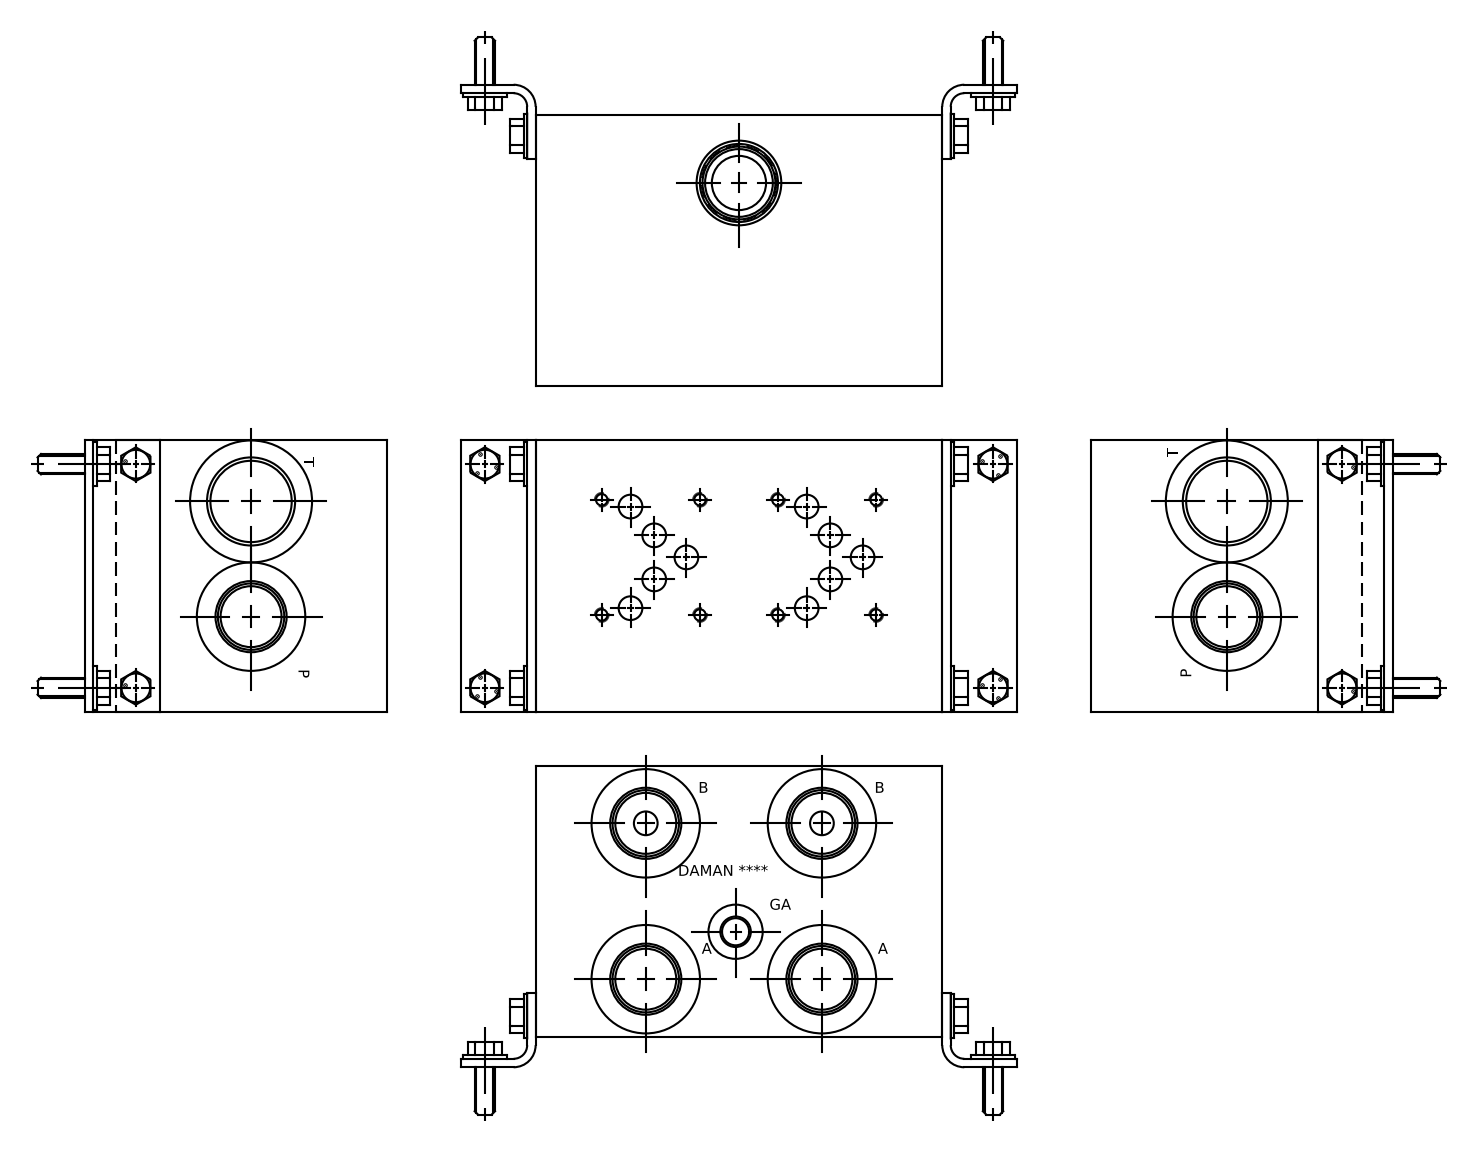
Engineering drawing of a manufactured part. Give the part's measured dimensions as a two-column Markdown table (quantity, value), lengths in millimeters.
| quantity | value |
| --- | --- |
| part name | Part_AD05JP023S_S_3D |
| STEP written by | Autodesk Inventor 2020 (AUTOMOTIVE_DESIGN) |
| units | millimeters |
| bodies | 1 solid, 714 faces (373 planar, 88 cylindrical, 253 other) |
| overall size | 190.5 × 127 × 127 |
| volume | 2 712 000 mm³ |
| surface area | 175 944 mm² |
| round holes (diameter × count) | 5.11 × 8, 6.35 × 8, 31.27 × 5, 33.34 × 5, 33.76 × 5, 48.97 × 5, 9.53 × 4, 10.31 × 4, 11.13 × 4, 28.57 × 4, 35.51 × 3, 7.92 × 2 |
| main face-to-face distances | 127, 190.5, 0.79, 189.71, 126.21, 188.92, 19.05, 19.84, 170.66, 107.16 |
| hole center spacings | 82.55, 18.28, 35.4, 35.89, 53.97, 60.3, 82.56, 17.48 |
